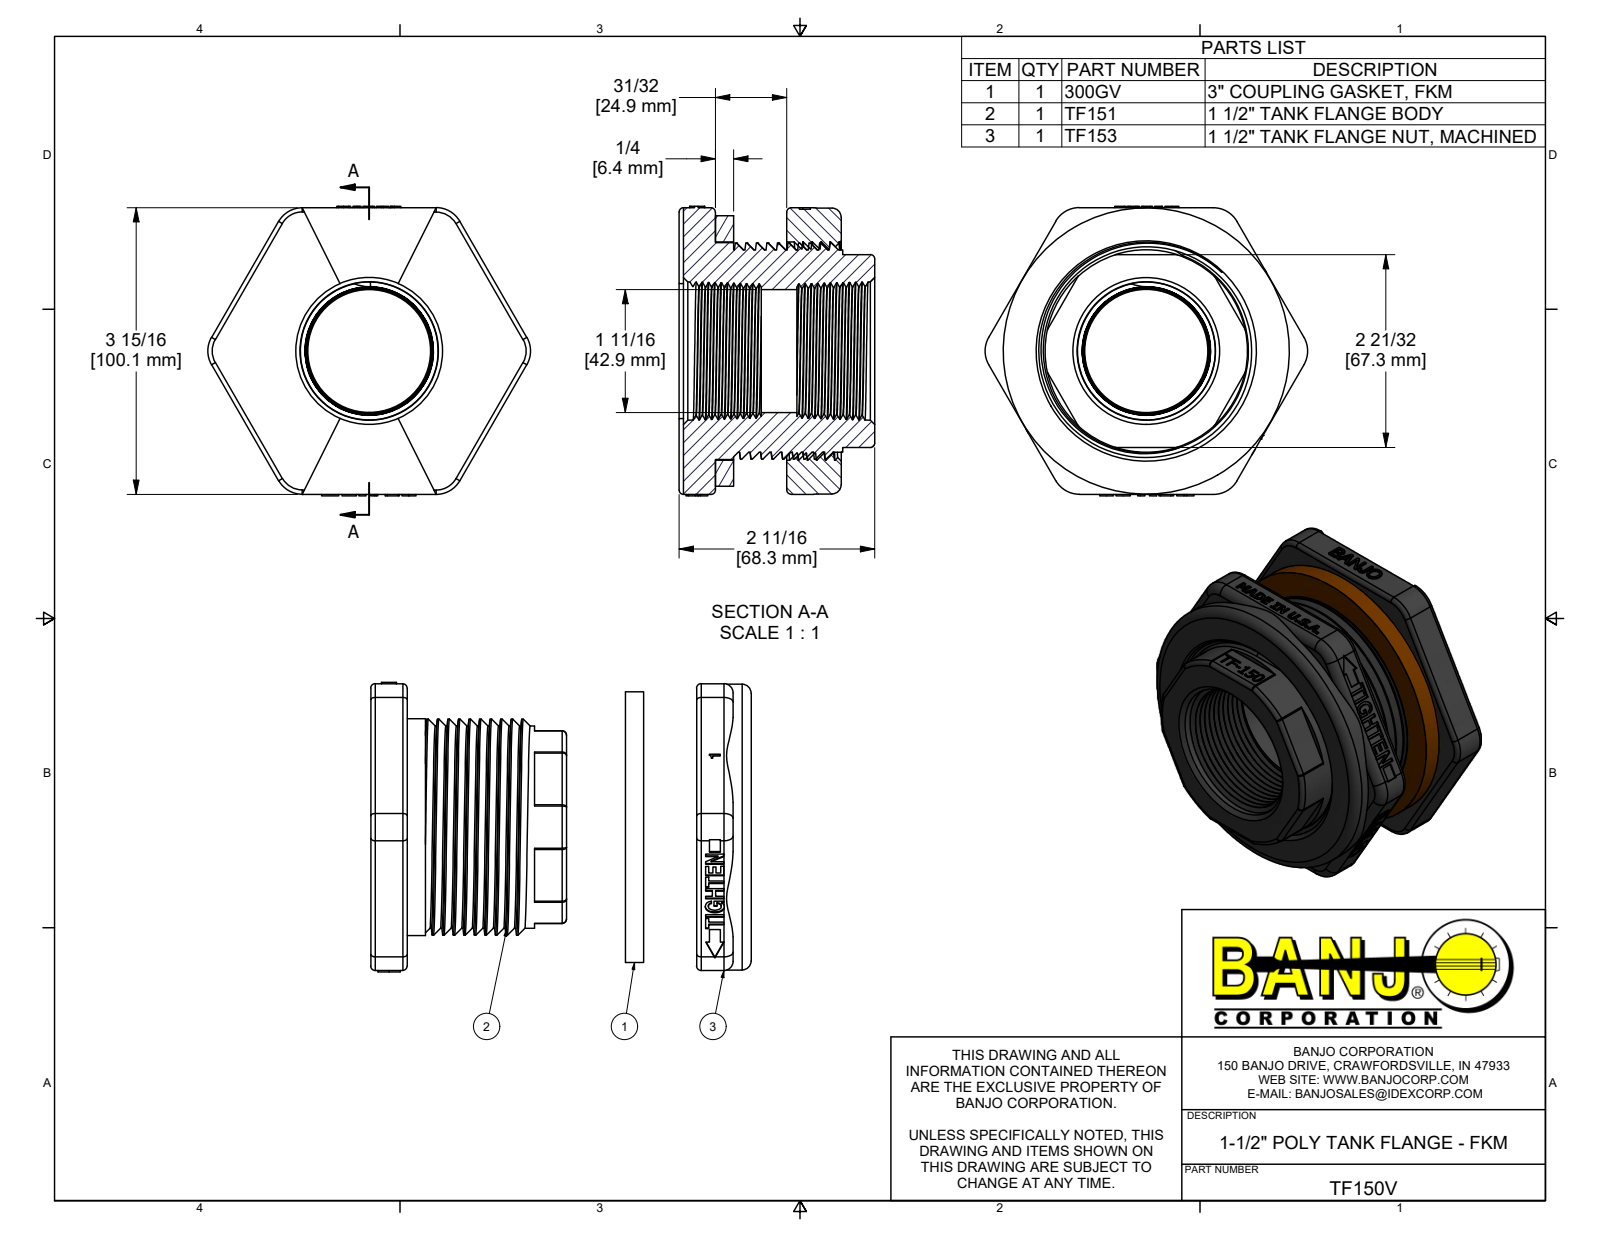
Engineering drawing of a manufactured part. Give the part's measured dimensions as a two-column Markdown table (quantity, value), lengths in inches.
| quantity | value |
| --- | --- |
| part name | TF150V; TF151; TF153; TF153X (+1 more) |
| STEP written by | Autodesk Inventor 2019 (AUTOMOTIVE_DESIGN) |
| units | inches |
| bodies | 3 solids, 848 faces (508 planar, 100 cylindrical, 240 other) |
| overall size | 58.629 × 4.434 × 3.98 |
| volume | 18.64 in³ |
| surface area | 478.8 in² |
| round holes (diameter × count) | 1.69 × 1, 2.807 × 1, 3 × 1 |
| round bosses / shafts (diameter × count) | 3.93 × 1, 3.719 × 1, 2.98 × 1, 2.97 × 1, 2.78 × 1 |
| partial cylindrical surfaces (radius × count) | 0.06 × 30, 0.062 × 6, 0.125 × 6, 0.375 × 6, 0.539 × 1, 0.79 × 1, 0.846 × 1, 1.01 × 1 |
| main face-to-face distances | 1.48, 0.75, 0.5, 0.98, 0.25, 0.73, 2.23, 1.73, 3.94, 0.44 |
